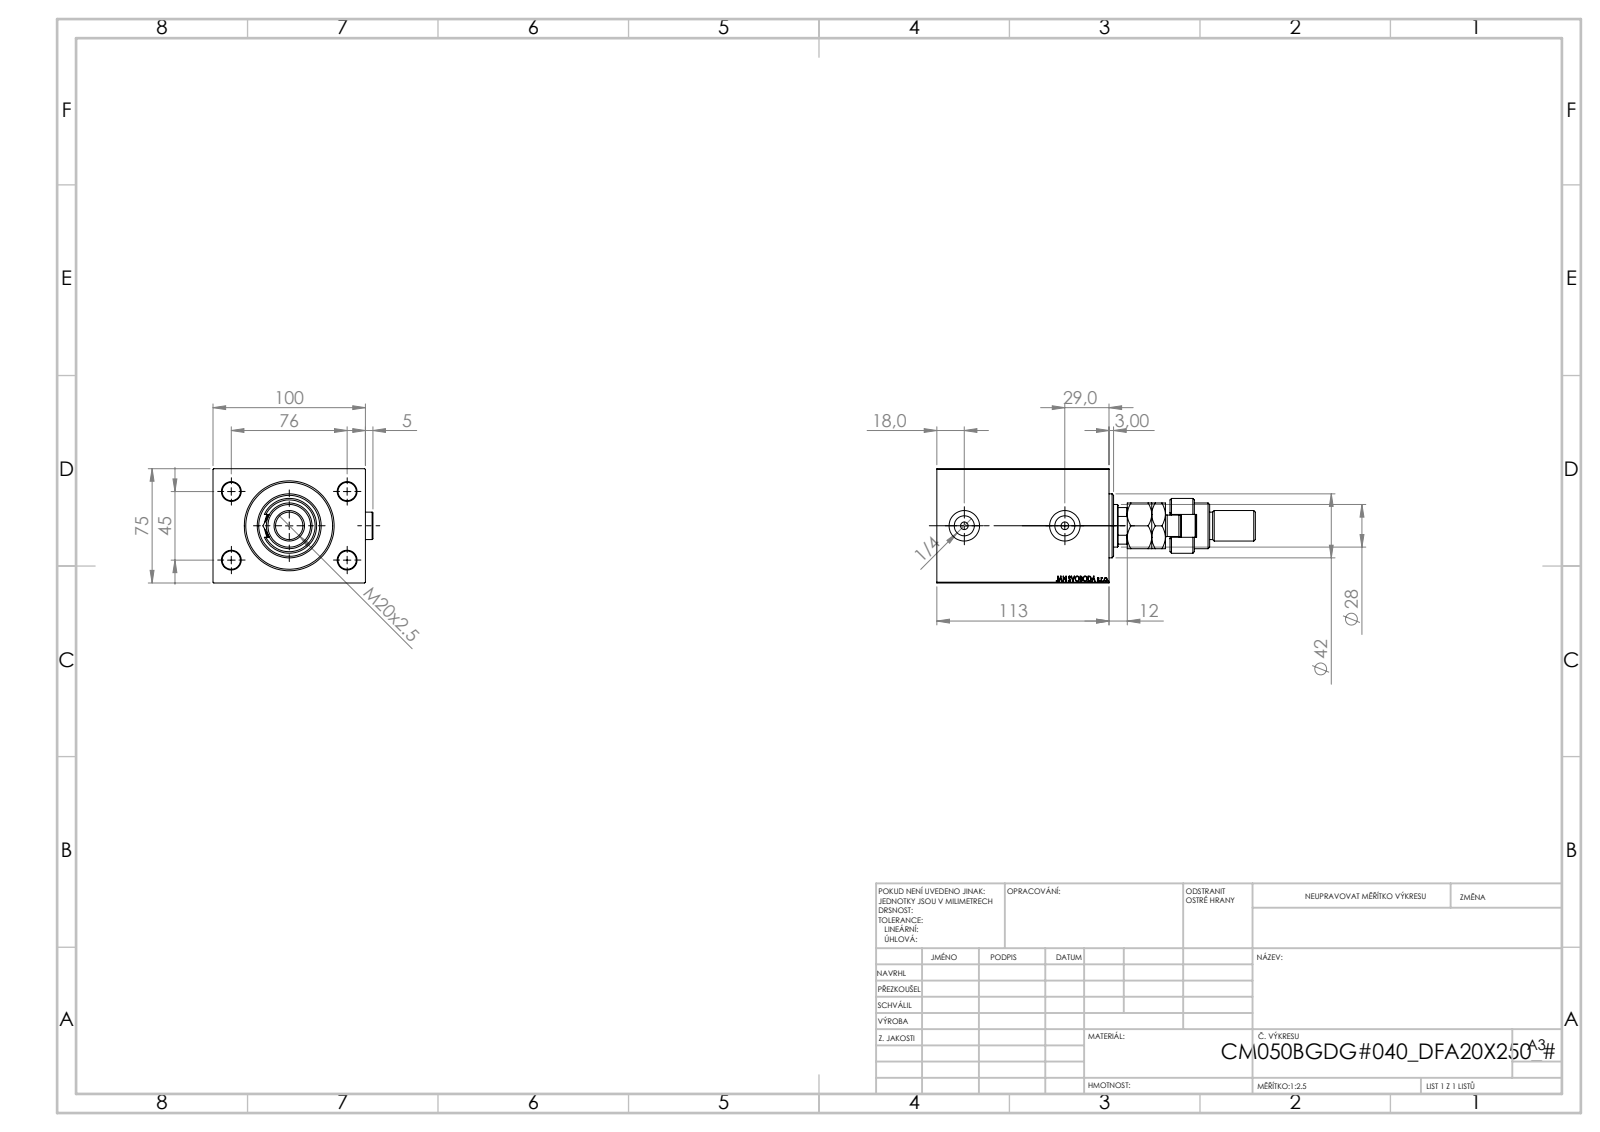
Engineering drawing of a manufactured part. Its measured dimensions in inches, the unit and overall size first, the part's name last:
Units: inches
Overall size (bounding box): 8.228 × 4.13 × 2.953
Round holes (diameter × count): ⌀0.472 ×4, ⌀0.197 ×2, ⌀0.518 ×2, ⌀0.787 ×2, ⌀0.728 ×1, ⌀1.102 ×1, ⌀1.24 ×1, ⌀1.28 ×1, ⌀1.969 ×1, ⌀2.047 ×1, ⌀2.244 ×1
Round bosses / shafts (diameter × count): ⌀0.709 ×3, ⌀1.654 ×1, ⌀1.417 ×1, ⌀1.181 ×1, ⌀0.866 ×1, ⌀0.787 ×1, ⌀0.551 ×1
Partial cylindrical surfaces — rounded edges, fillets, slot ends (radius × count): R0.295 ×1, R0.472 ×1, R0.531 ×1
Main face-to-face distances: 2.953, 3.937, 4.449, 3.898, 0.551, 0.472, 1.85, 2.047, 1.575, 3.976
Hole centre spacings: 1.739, 1.772, 2.992, 3.477, 2.598
Volume: 49.97 in³ · Surface area: 185.8 in²
Bodies: 7 solids, 1023 faces (464 planar, 85 cylindrical, 474 other)
Part name (STEP PRODUCT): Zatka_OIL_PORT; FEMALE_PART_FOR_DFA; V450CM_B_VCP; MFA (+2 more)
STEP written by: SolidWorks 2019 (CONFIG_CONTROL_DESIGN)
